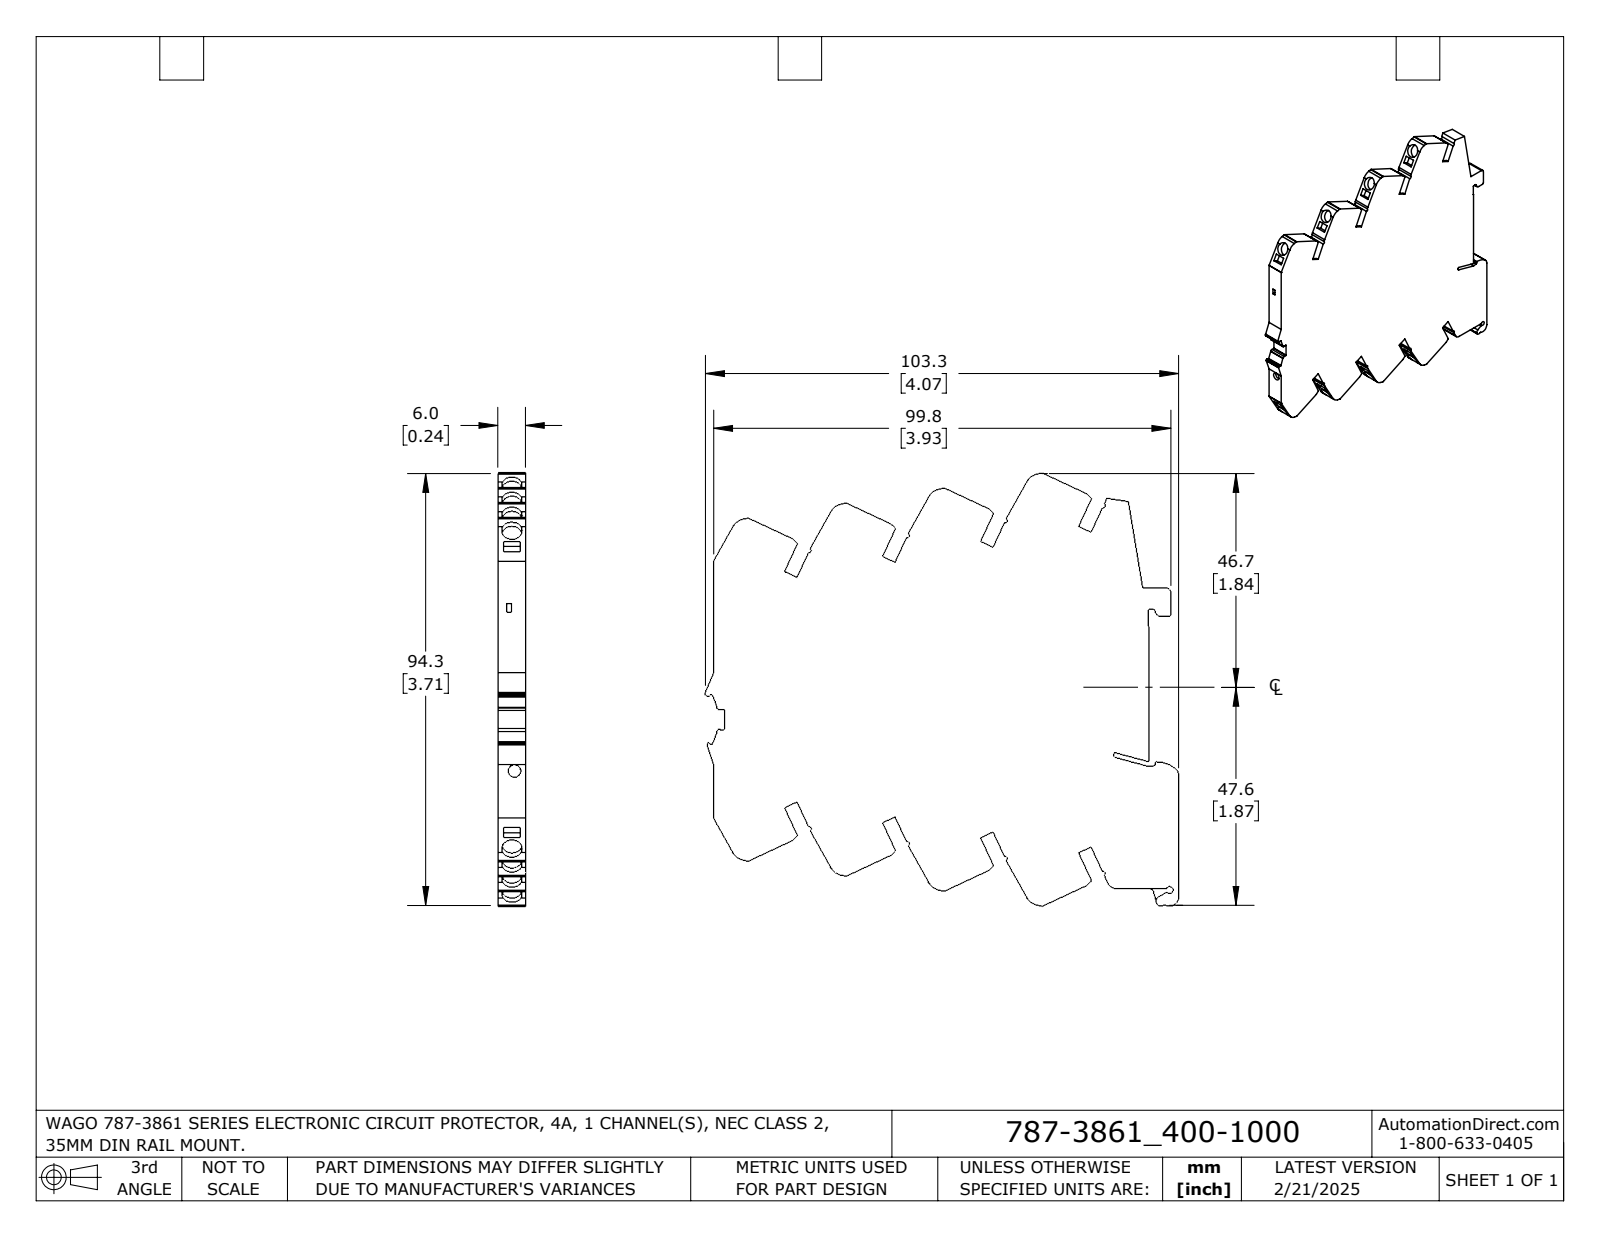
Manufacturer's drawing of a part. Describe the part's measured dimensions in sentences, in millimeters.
The part is named "787-3861_400-1000_HI". Its 3-D file was written by "SolidWorks 2024 (AUTOMOTIVE_DESIGN)". It is 1 solid with 262 faces: 197 planar, 65 cylindrical and 0 other. Overall it measures 103.3 by 94.26 by 6 millimeters. Its volume is 43 992 cubic millimeters and its surface area 18 864 square millimeters. Round holes: 8 of diameter 4.4, 1 of diameter 2.7. Partial cylindrical surfaces (rounded edges, fillets, slot ends): 13 of radius 0.2, 12 of radius 0.5, 8 of radius 0.4, 8 of radius 3.35, 5 of radius 1, 3 of radius 0.3, 3 of radius 2, 2 of radius 0.45. The main face-to-face distances are 6, 17.99, 17.02, 3, 35.98, 12.01, 20.99, 14.99, 34.04, 12. The hole center spacings are 13.35, 26.7, 13.34, 40.05, 26.71.
